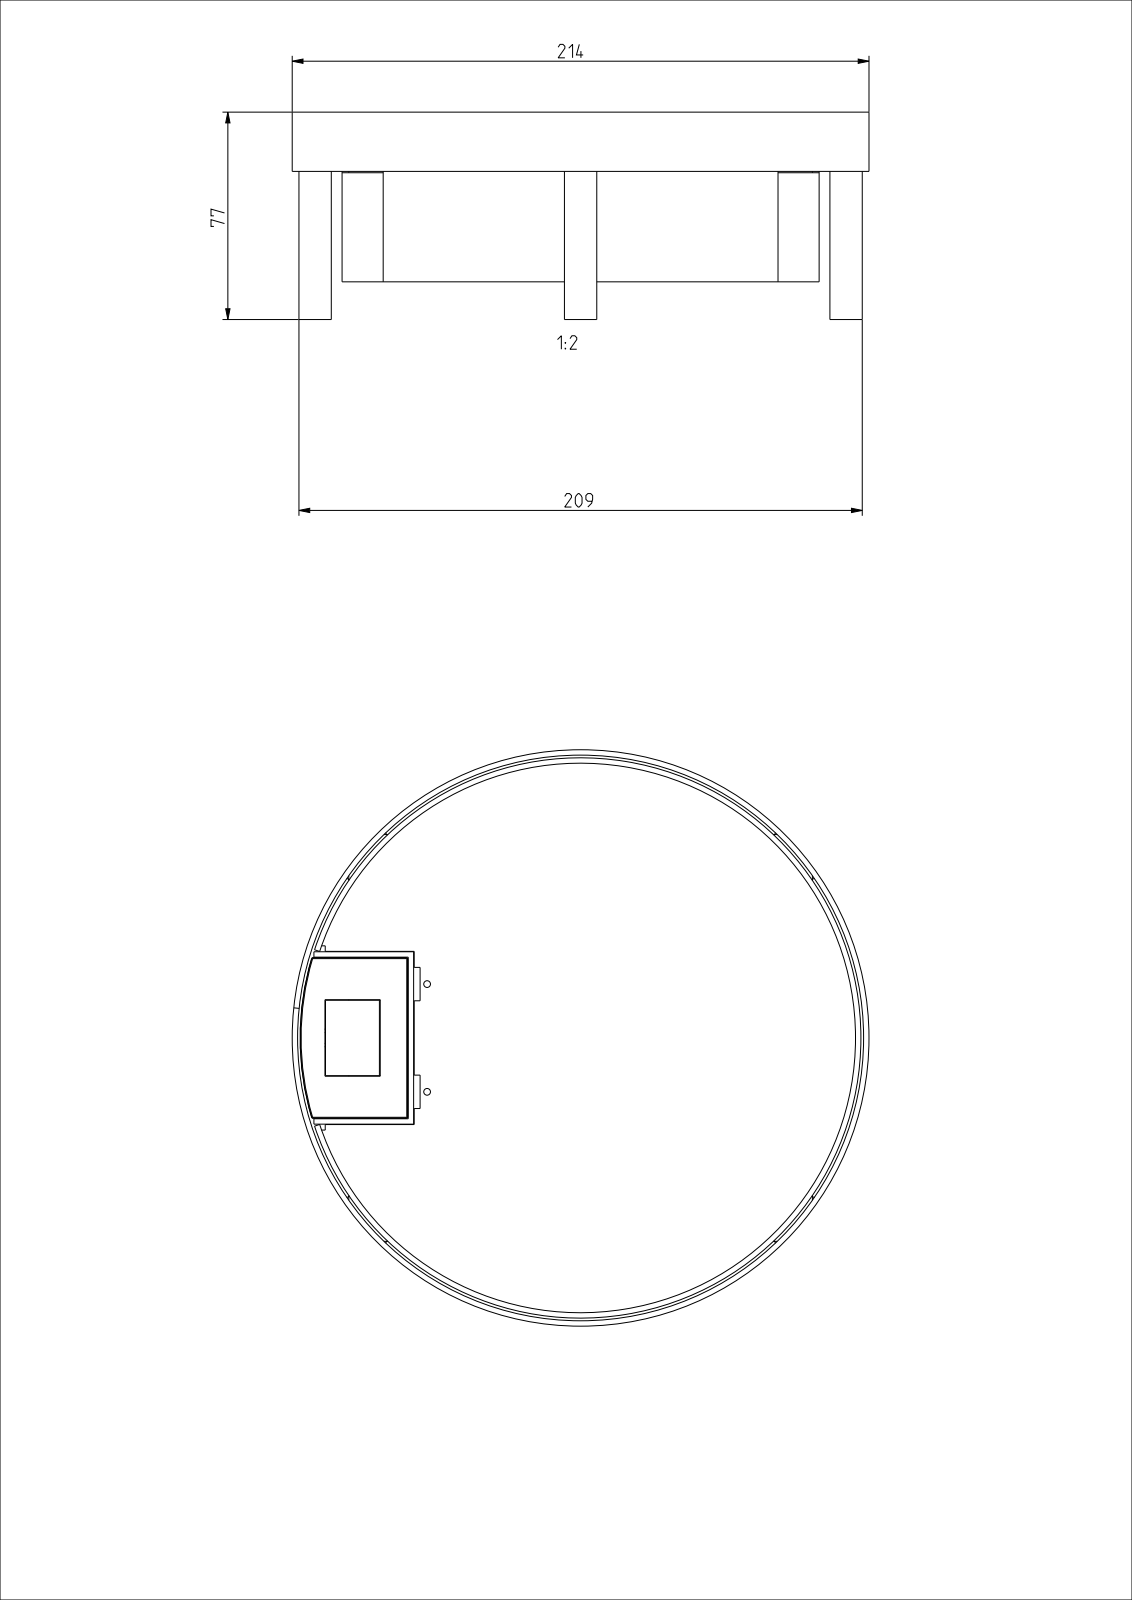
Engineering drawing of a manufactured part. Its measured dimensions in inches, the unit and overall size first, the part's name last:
Units: inches
Overall size (bounding box): 8.425 × 8.425 × 3.031
Round holes (diameter × count): ⌀0.15 ×6, ⌀0.268 ×4, ⌀0.335 ×4, ⌀0.398 ×4, ⌀0.098 ×2, ⌀8.268 ×1
Round bosses / shafts (diameter × count): ⌀0.472 ×4, ⌀0.388 ×4, ⌀8.425 ×1, ⌀8.189 ×1, ⌀8.031 ×1
Partial cylindrical surfaces — rounded edges, fillets, slot ends (radius × count): R0.02 ×10, R0.012 ×3, R0.04 ×1, R0.26 ×1
Main face-to-face distances: 0.079, 0.098, 0.197, 6.043, 0.276, 0.118, 6.87, 0.669, 5.945, 6.142
Hole centre spacings: 1.62, 3.834, 3.878, 4.187, 5.484, 6.477, 7.54, 0.867
Volume: 13.16 in³ · Surface area: 338.8 in²
Bodies: 15 solids, 290 faces (187 planar, 85 cylindrical, 18 other)
Part name (STEP PRODUCT): T-00671; T-00672; T-00673; T-00674 (+8 more)
STEP written by: CREO PARAMETRIC BY PTC INC, 2022024 (AUTOMOTIVE_DESIGN)
